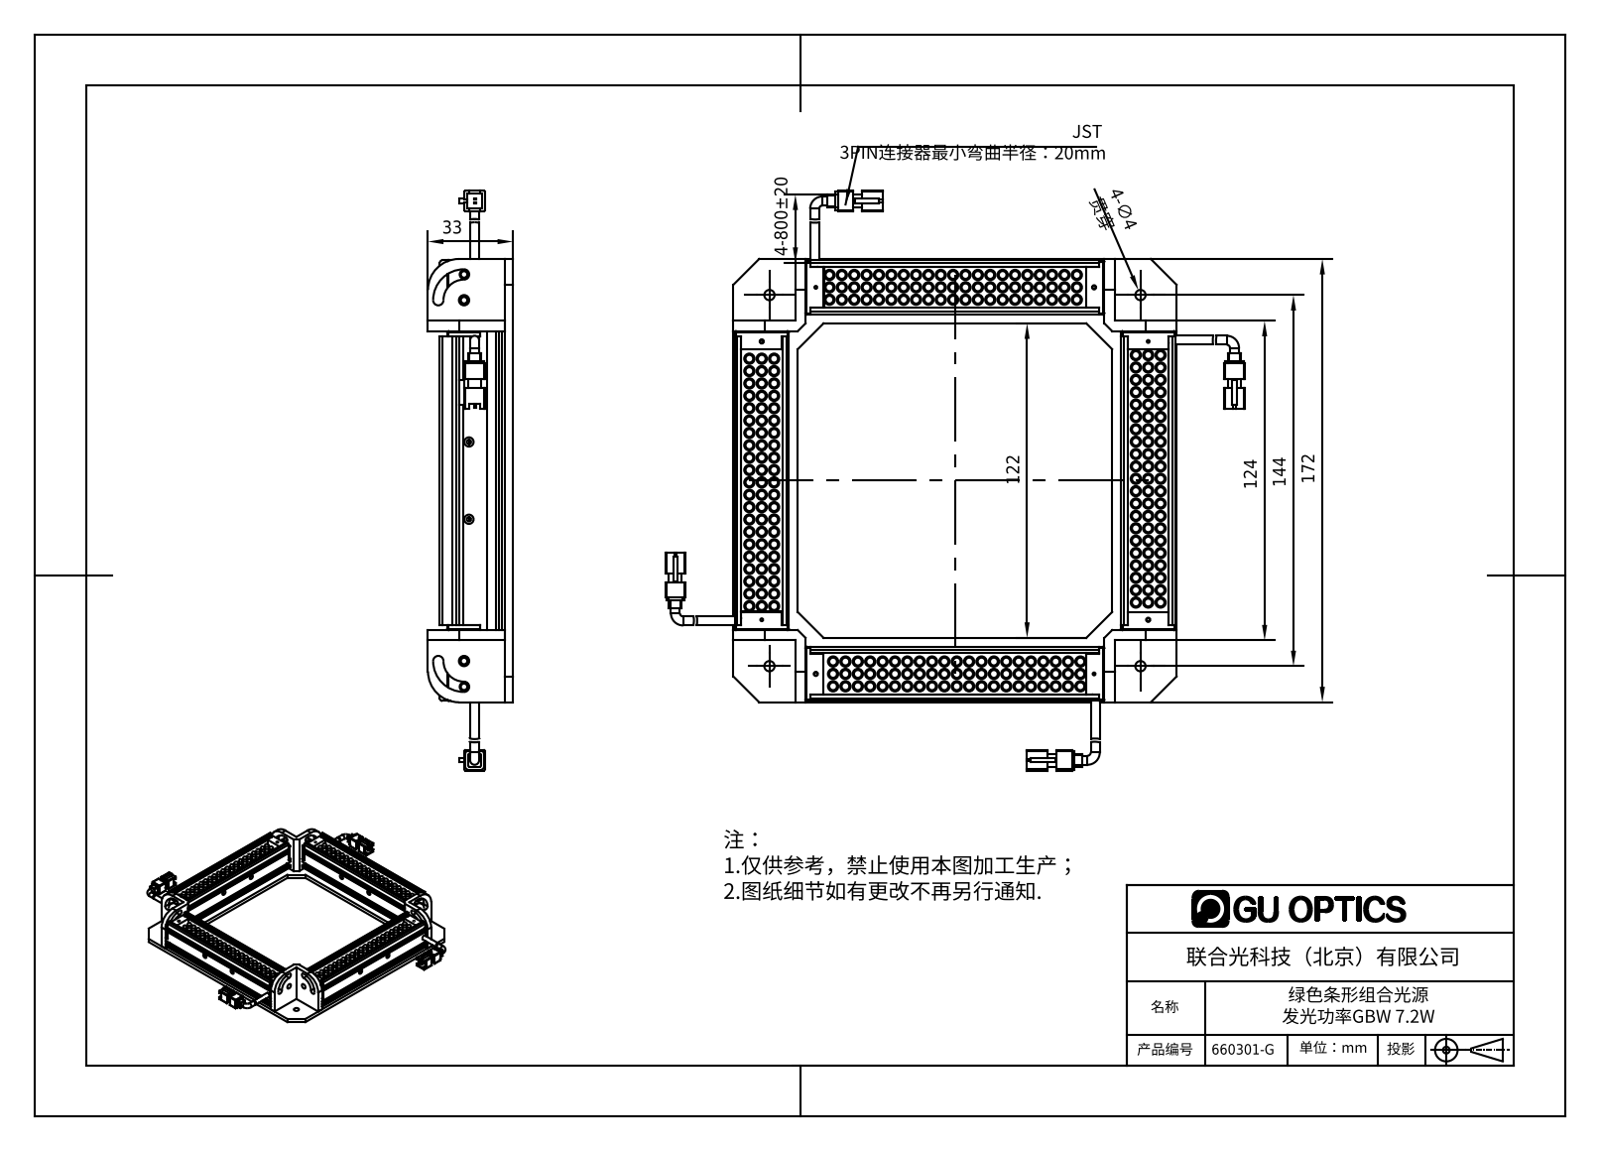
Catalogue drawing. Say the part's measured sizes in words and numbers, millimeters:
The part is named "660301-G". Its 3-D file was written by "SolidWorks 2016 (AUTOMOTIVE_DESIGN)". It is 29 solids with 2961 faces: 1092 planar, 1376 cylindrical and 493 other. Overall it measures 225 by 225 by 33 millimeters. Its volume is 184 233 cubic millimeters and its surface area 167 692 square millimeters. Round holes: 12 of diameter 1.6, 8 of diameter 2.5, 8 of diameter 3, 8 of diameter 4, 4 of diameter 1.1, 4 of diameter 1.25, 4 of diameter 1.7, 4 of diameter 2. Round bosses or shafts: 252 of diameter 4, 252 of diameter 3, 8 of diameter 3.5. Partial cylindrical surfaces (rounded edges, fillets, slot ends): 48 of radius 1, 32 of radius 0.5, 8 of radius 2, 8 of radius 12, 4 of radius 1.65, 4 of radius 8. The main face-to-face distances are 2.5, 3, 18.5, 150, 4, 21, 147.5, 1, 9.9, 6.5. The hole center spacings are 16.38, 18.25, 26.23, 108, 124.05, 126.04, 130.7, 134.05.
